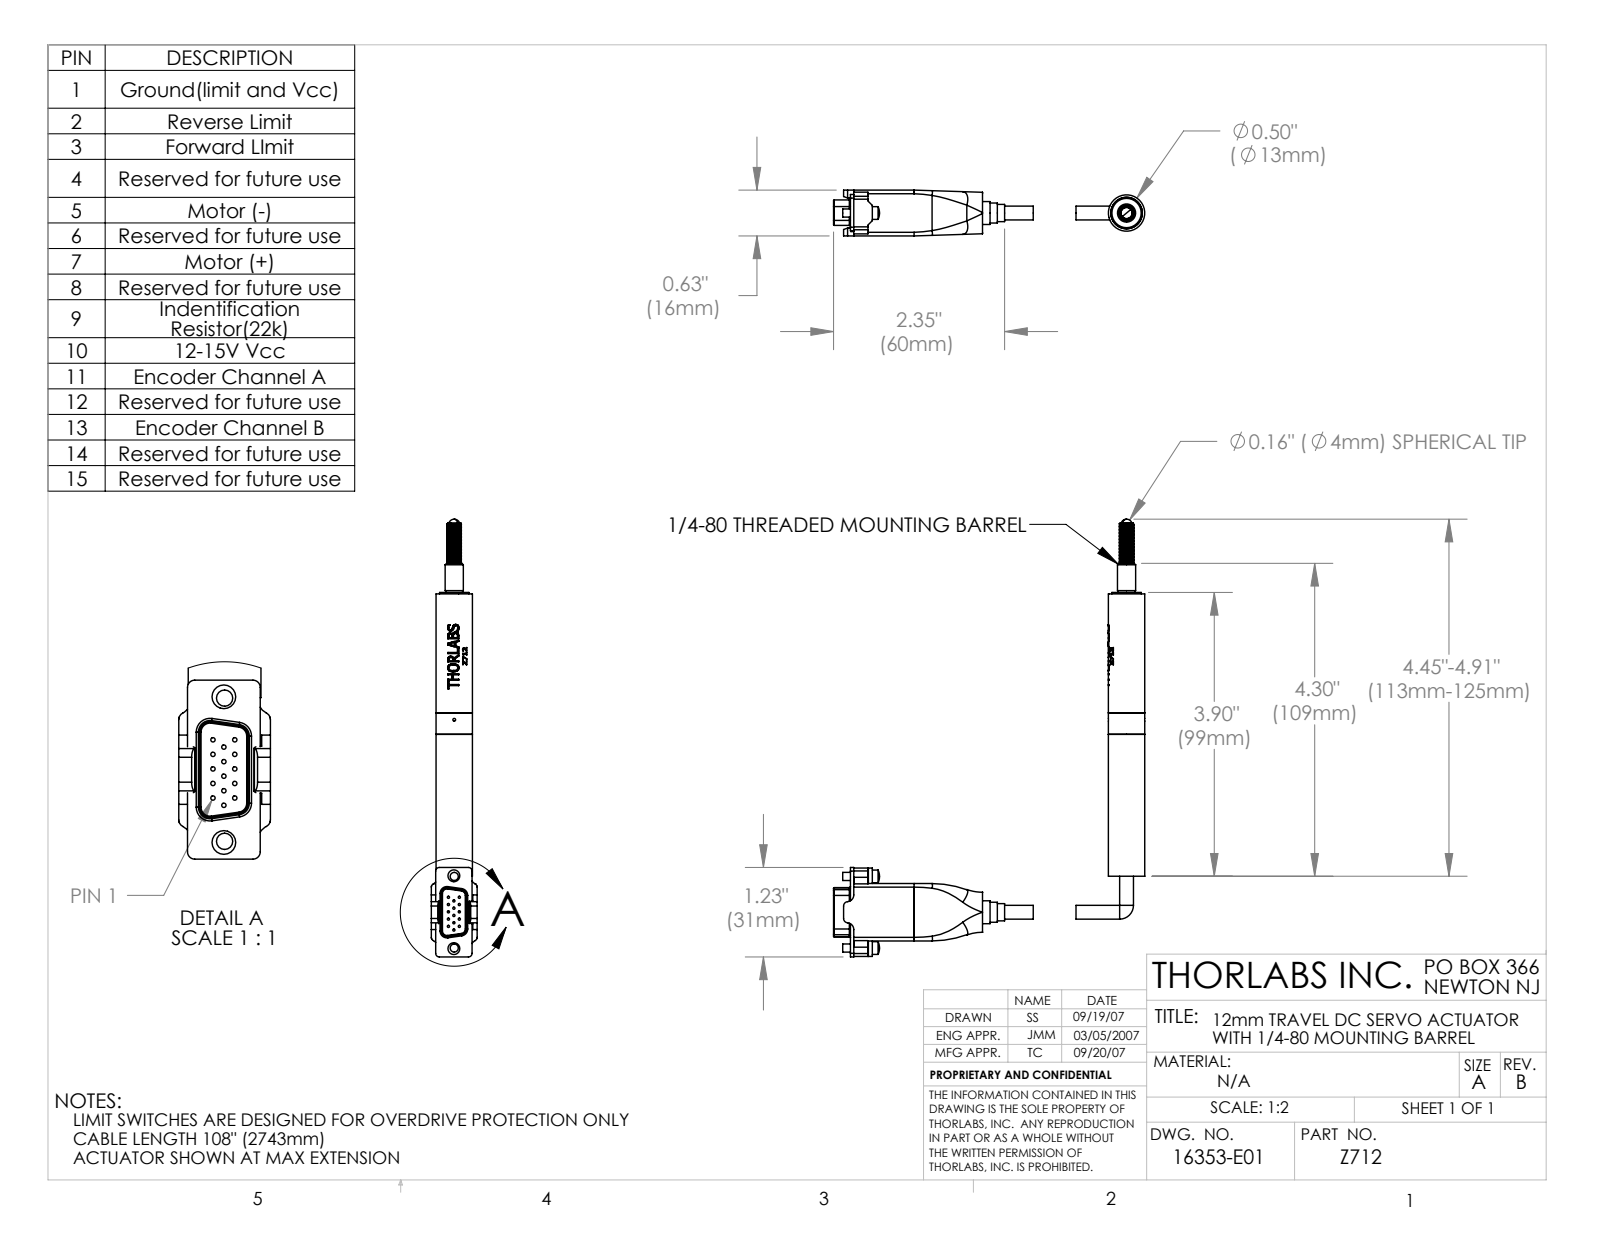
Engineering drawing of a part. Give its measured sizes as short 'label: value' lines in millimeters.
name: Ball156GR440; 16352-001; z7cable; 16353-E0W (+8 more)
written by: SolidWorks 2007 (CONFIG_CONTROL_DESIGN)
unit: mm
bodies: 12 solids, 1026 faces (384 planar, 473 cylindrical, 169 other)
size: 146.7 × 108.7 × 16
volume: 23 780 mm³; area: 23 320 mm²
holes: 15× ⌀0.5, 2× ⌀1, 2× ⌀4.1, 1× ⌀1, 1× ⌀1.3, 1× ⌀1.6, 1× ⌀2, 1× ⌀2.4, 1× ⌀4, 1× ⌀4.6, 1× ⌀4.8, 1× ⌀4.8
bosses: 15× ⌀0.8, 2× ⌀4.4, 2× ⌀2.8, 1× ⌀14, 1× ⌀12.7, 1× ⌀12.2, 1× ⌀11.2, 1× ⌀10.2
rounds: 8× R0.3, 8× R0.4, 8× R1, 6× R0.5, 6× R1.3, 6× R1.5, 6× R1.6, 4× R0.1
face distances: 16, 20.1, 2.2, 4.4, 13.8, 1.2, 5.6, 0.5, 3.6, 2.5
hole spacings: 2.3, 4.3, 2.5, 6.6, 5.1, 4.6, 6.4, 7.6
